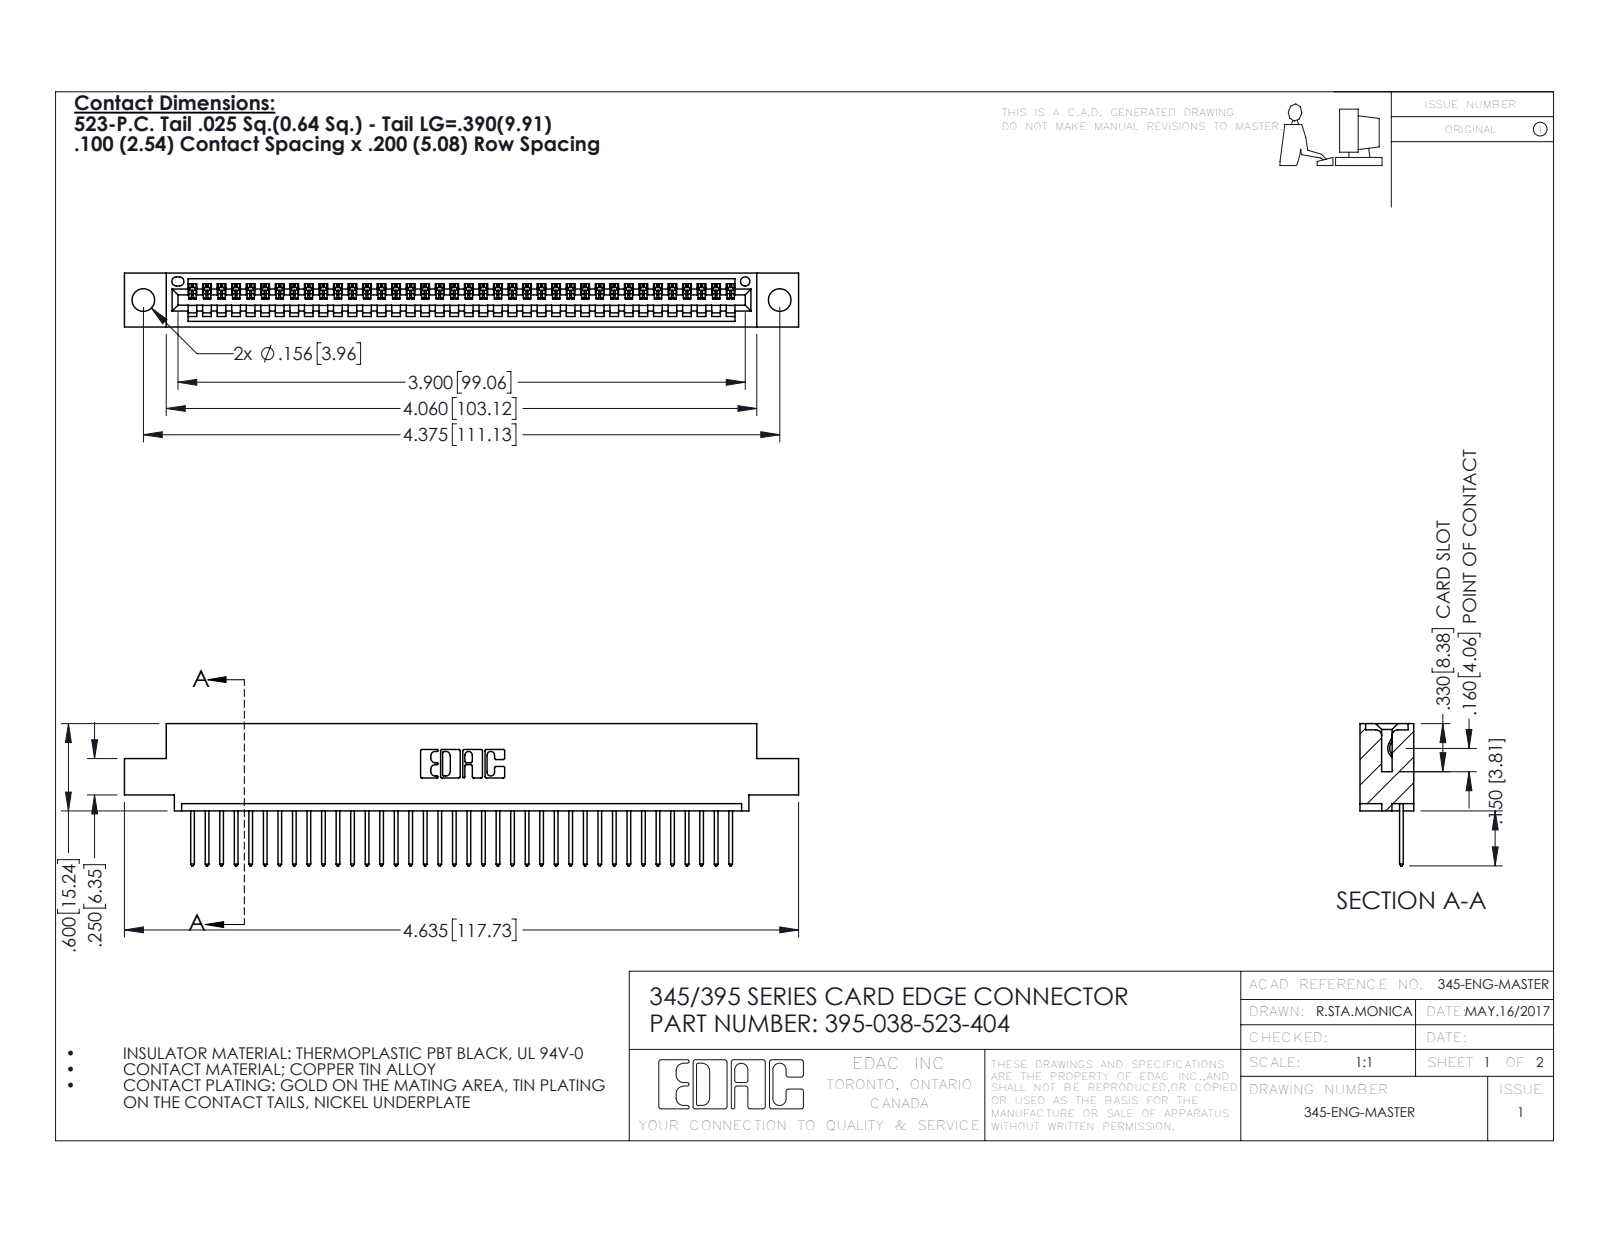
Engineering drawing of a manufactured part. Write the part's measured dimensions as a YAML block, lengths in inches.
part_name: "345-292-001_345-293-123; 395-038-523-404; 345 Part_0.110 Offset - 0.156 Dia-TH"
step_written_by: "SolidWorks 2016 (CONFIG_CONTROL_DESIGN)"
units: inches
bodies: {solids: 39, faces: 2334, planar: 1604, cylindrical: 730, other: 0}
overall_size: [4.635, 0.977, 0.37]
volume: 0.67
surface_area: 22.41
round_holes:
  - {diameter: 0.156, count: 2}
  - {diameter: 0.064, count: 1}
partial_cylinders:
  - {radius: 0.006, count: 76}
  - {radius: 0.01, count: 76}
  - {radius: 0.01, count: 22}
  - {radius: 0.007, count: 6}
  - {radius: 0.031, count: 6}
  - {radius: 0.026, count: 3}
  - {radius: 0.031, count: 2}
  - {radius: 0.04, count: 2}
face_to_face_distances: [0.072, 0.298, 0.37, 0.2, 0.098, 0.272, 0.025, 0.225, 0.149, 0.072]
hole_center_spacings: [0.27, 4.139, 4.375]
